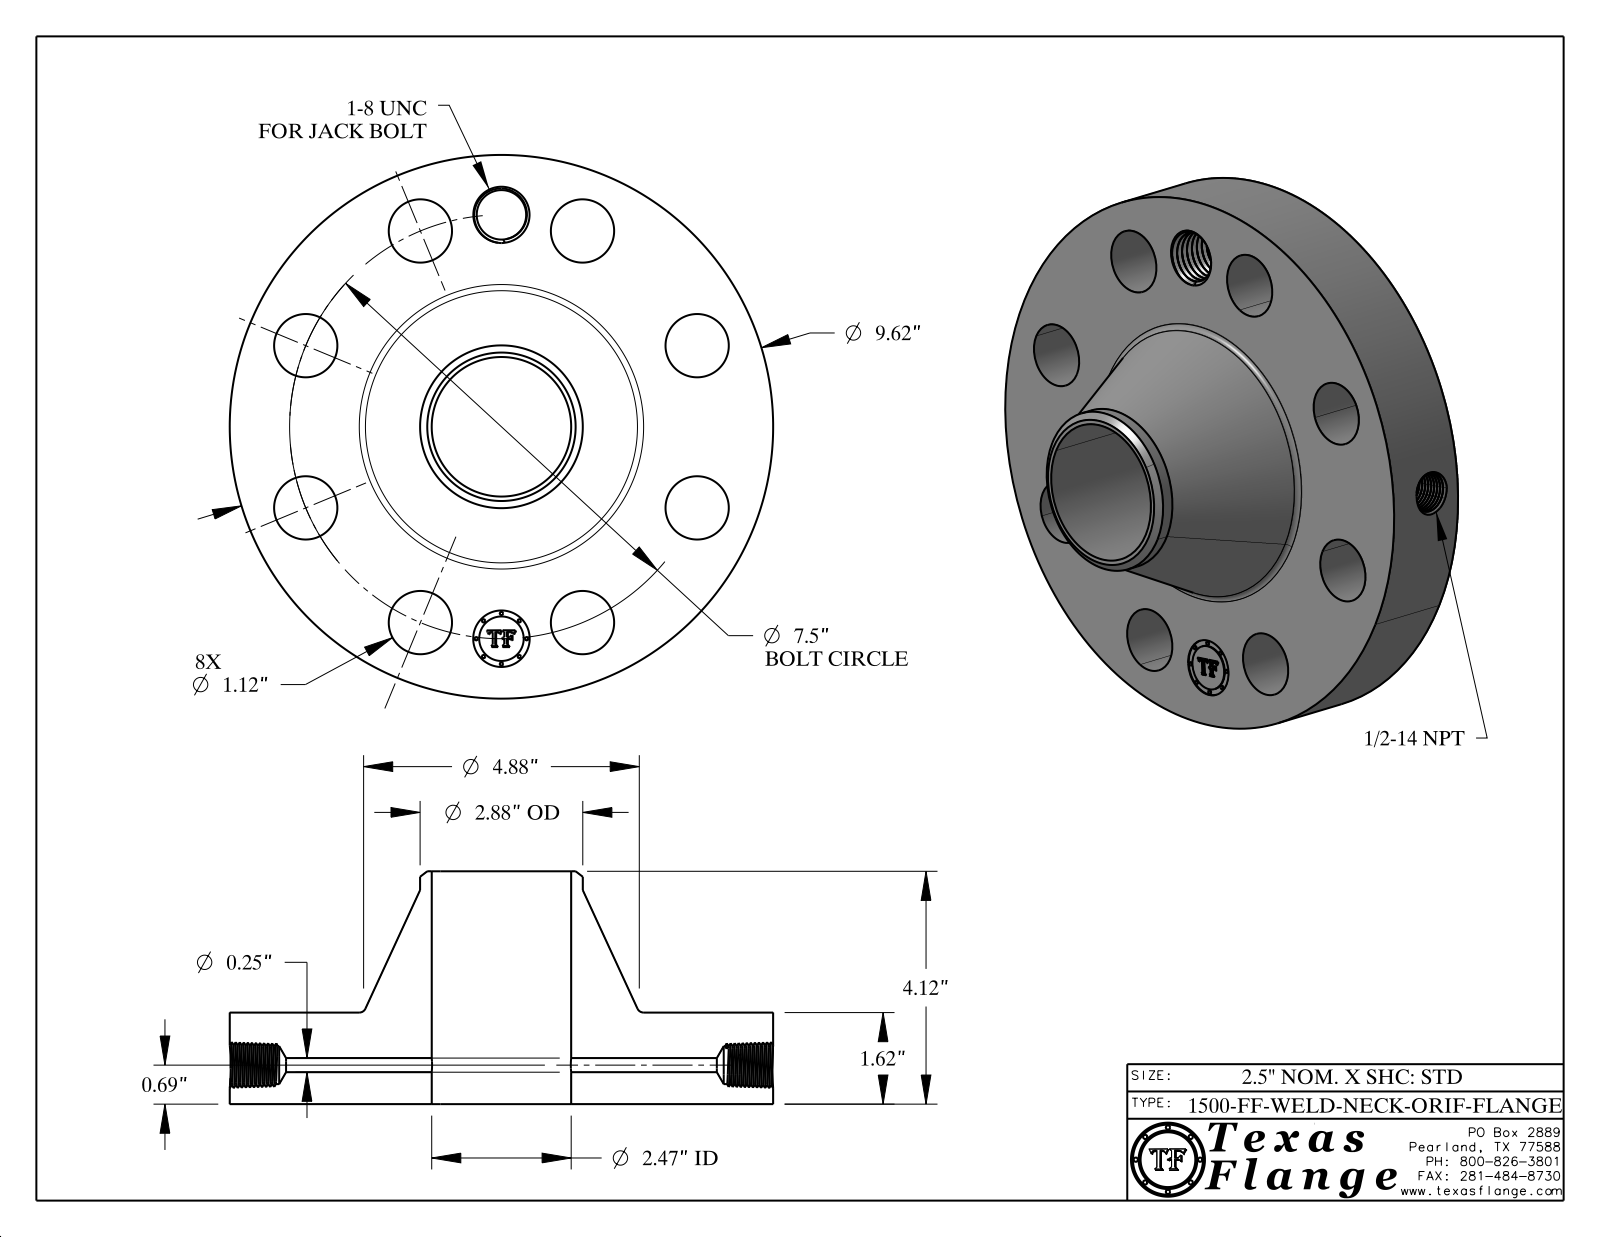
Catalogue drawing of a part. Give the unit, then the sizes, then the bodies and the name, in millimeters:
Units: millimetres
Overall size (bounding box): 244.3 × 244.3 × 104.6
Round holes (diameter × count): ⌀28.4 ×8, ⌀6.4 ×1, ⌀17.1 ×1, ⌀22.2 ×1, ⌀25.4 ×1, ⌀62.7 ×1
Round bosses / shafts (diameter × count): ⌀1.5 ×8, ⌀244.3 ×1, ⌀73.2 ×1, ⌀20 ×1
Main face-to-face distances: 41.1, 104.6, 63.5, 40.8, 0.4, 63.9, 7.6, 7.4, 1.4, 6.3
Hole centre spacings: 95.3, 72.9, 134.7, 176, 190.5, 37.2, 105.8, 158.4
Volume: 1 826 000 mm³ · Surface area: 181 900 mm²
Bodies: 1 solid, 756 faces (368 planar, 87 cylindrical, 301 other)
Part name (STEP PRODUCT): 1500-FF-WELD-NECK
STEP written by: CATIA V5 STEP AP214 (AUTOMOTIVE_DESIGN)
